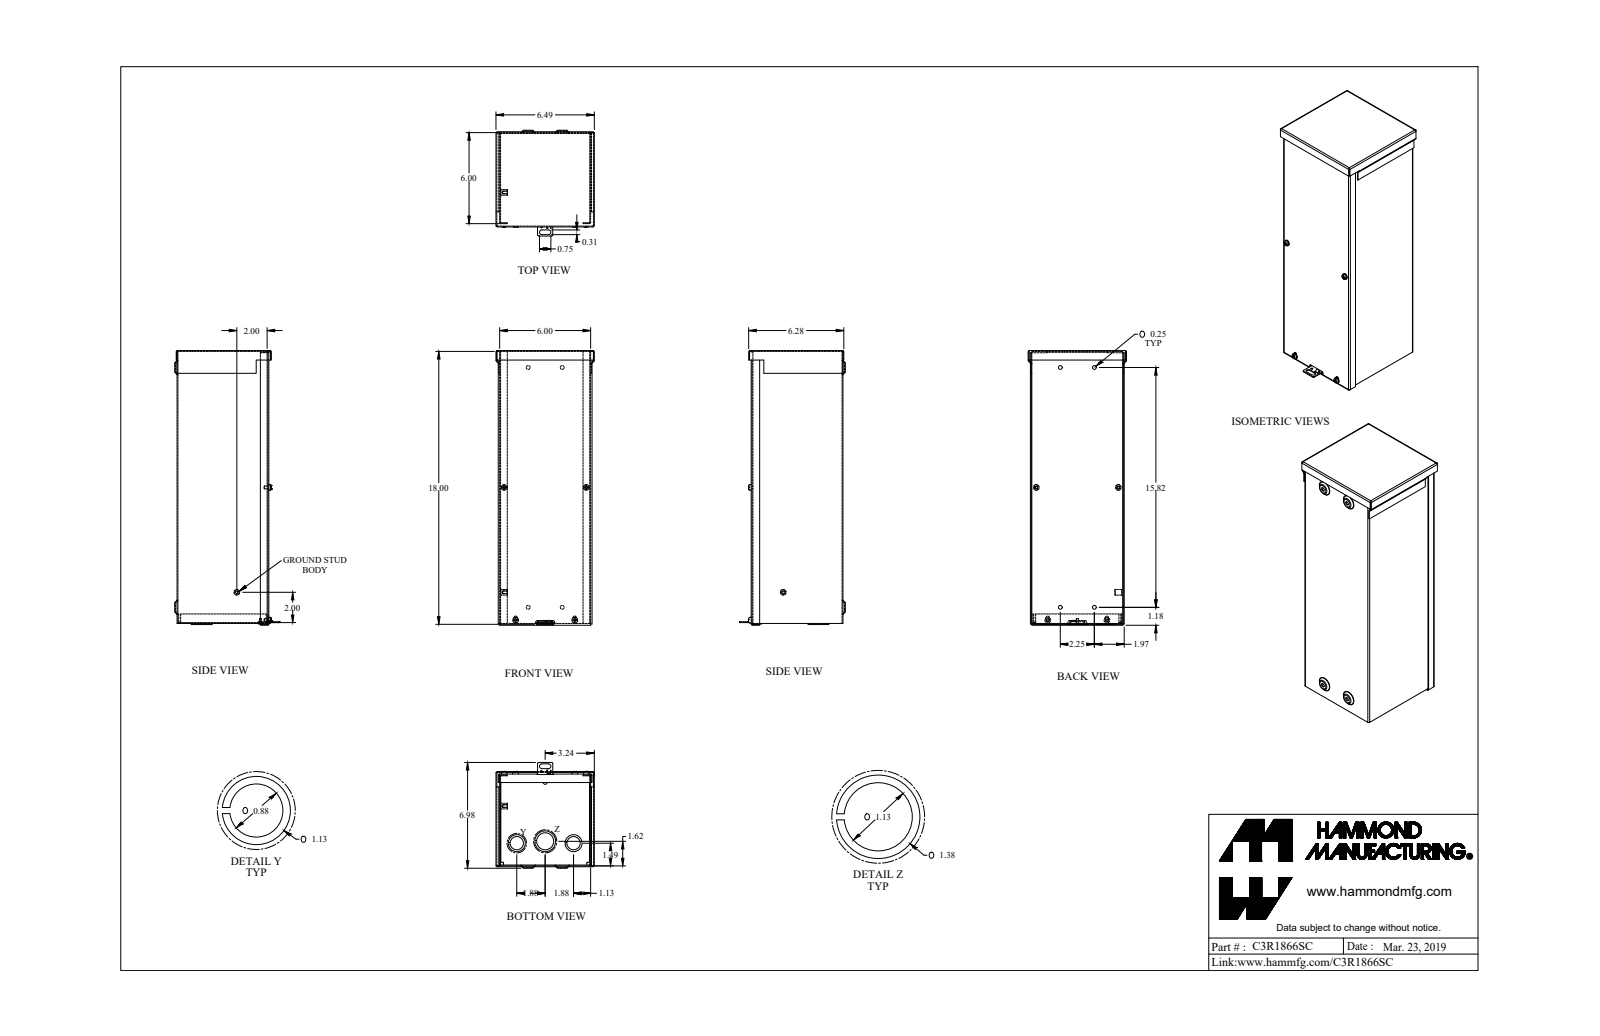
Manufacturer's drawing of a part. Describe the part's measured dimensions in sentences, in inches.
The part is named "C3R1866SC_Default". Its 3-D file was written by "SolidWorks 2019 (CONFIG_CONTROL_DESIGN)". It is 11 solids with 419 faces: 220 planar, 113 cylindrical and 86 other. Overall it measures 18.12 by 6.977 by 6.489 inches. Its volume is 33.24 cubic inches and its surface area 1 175 square inches. Round holes: 4 of diameter 0.17, 4 of diameter 0.25, 2 of diameter 0.875, 1 of diameter 0.125, 1 of diameter 0.137, 1 of diameter 0.156, 1 of diameter 1.125. Round bosses or shafts: 4 of diameter 0.375, 4 of diameter 0.19, 2 of diameter 1.125, 1 of diameter 1.375, 1 of diameter 0.375, 1 of diameter 0.125. Partial cylindrical surfaces (rounded edges, fillets, slot ends): 21 of radius 0.029, 21 of radius 0.086, 8 of radius 0.109, 8 of radius 0.125, 2 of radius 0.156. The main face-to-face distances are 0.057, 5.943, 6, 5.886, 6.057, 0.057, 17.886, 17.943, 17.943, 18. The hole center spacings are 8.066, 8.789, 2.25, 8.711, 15.818, 15.977, 16.608, 0.763.
